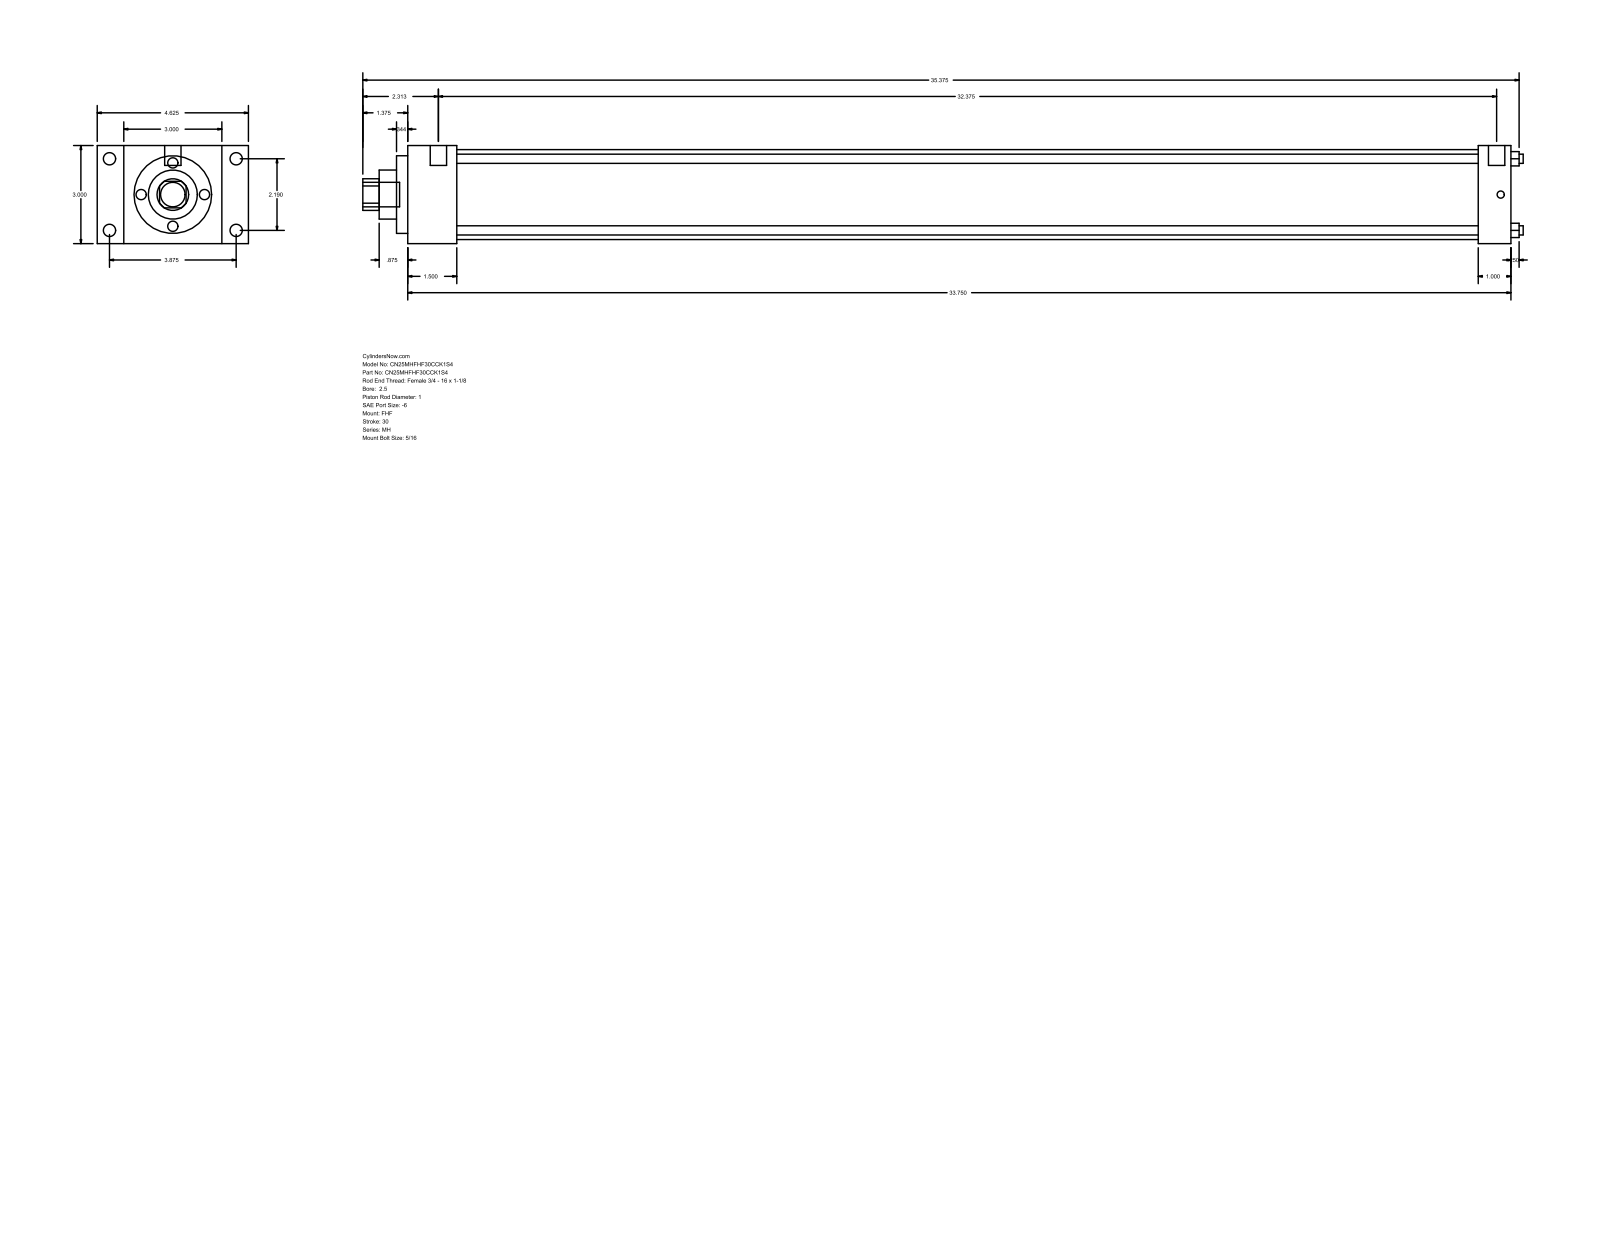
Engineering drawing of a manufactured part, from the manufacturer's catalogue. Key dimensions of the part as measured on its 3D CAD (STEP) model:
Part name (STEP PRODUCT): MH_FHF__0250_1
STEP written by: GSSL Pune (CONFIG_CONTROL_DESIGN)
Units: millimetres
Bodies: 0 solids, 90 faces (61 planar, 29 cylindrical, 0 other)
Overall size (bounding box): 901.7 × 117.47 × 76.2
Round holes (diameter × count): ⌀7.14 ×4, ⌀25.4 ×1, ⌀38.1 ×1, ⌀60.33 ×1, ⌀69.85 ×1
Round bosses / shafts (diameter × count): ⌀9.53 ×4, ⌀5.56 ×4, ⌀12.7 ×2, ⌀19.05 ×1
Partial cylindrical surfaces — rounded edges, fillets, slot ends (radius × count): R12.29 ×1
Main face-to-face distances: 76.2, 857.25, 38.11, 819.14, 20.64, 96.84, 117.48, 831.85, 793.74, 25.4
Hole centre spacings: 39.33, 55.62, 78.66
